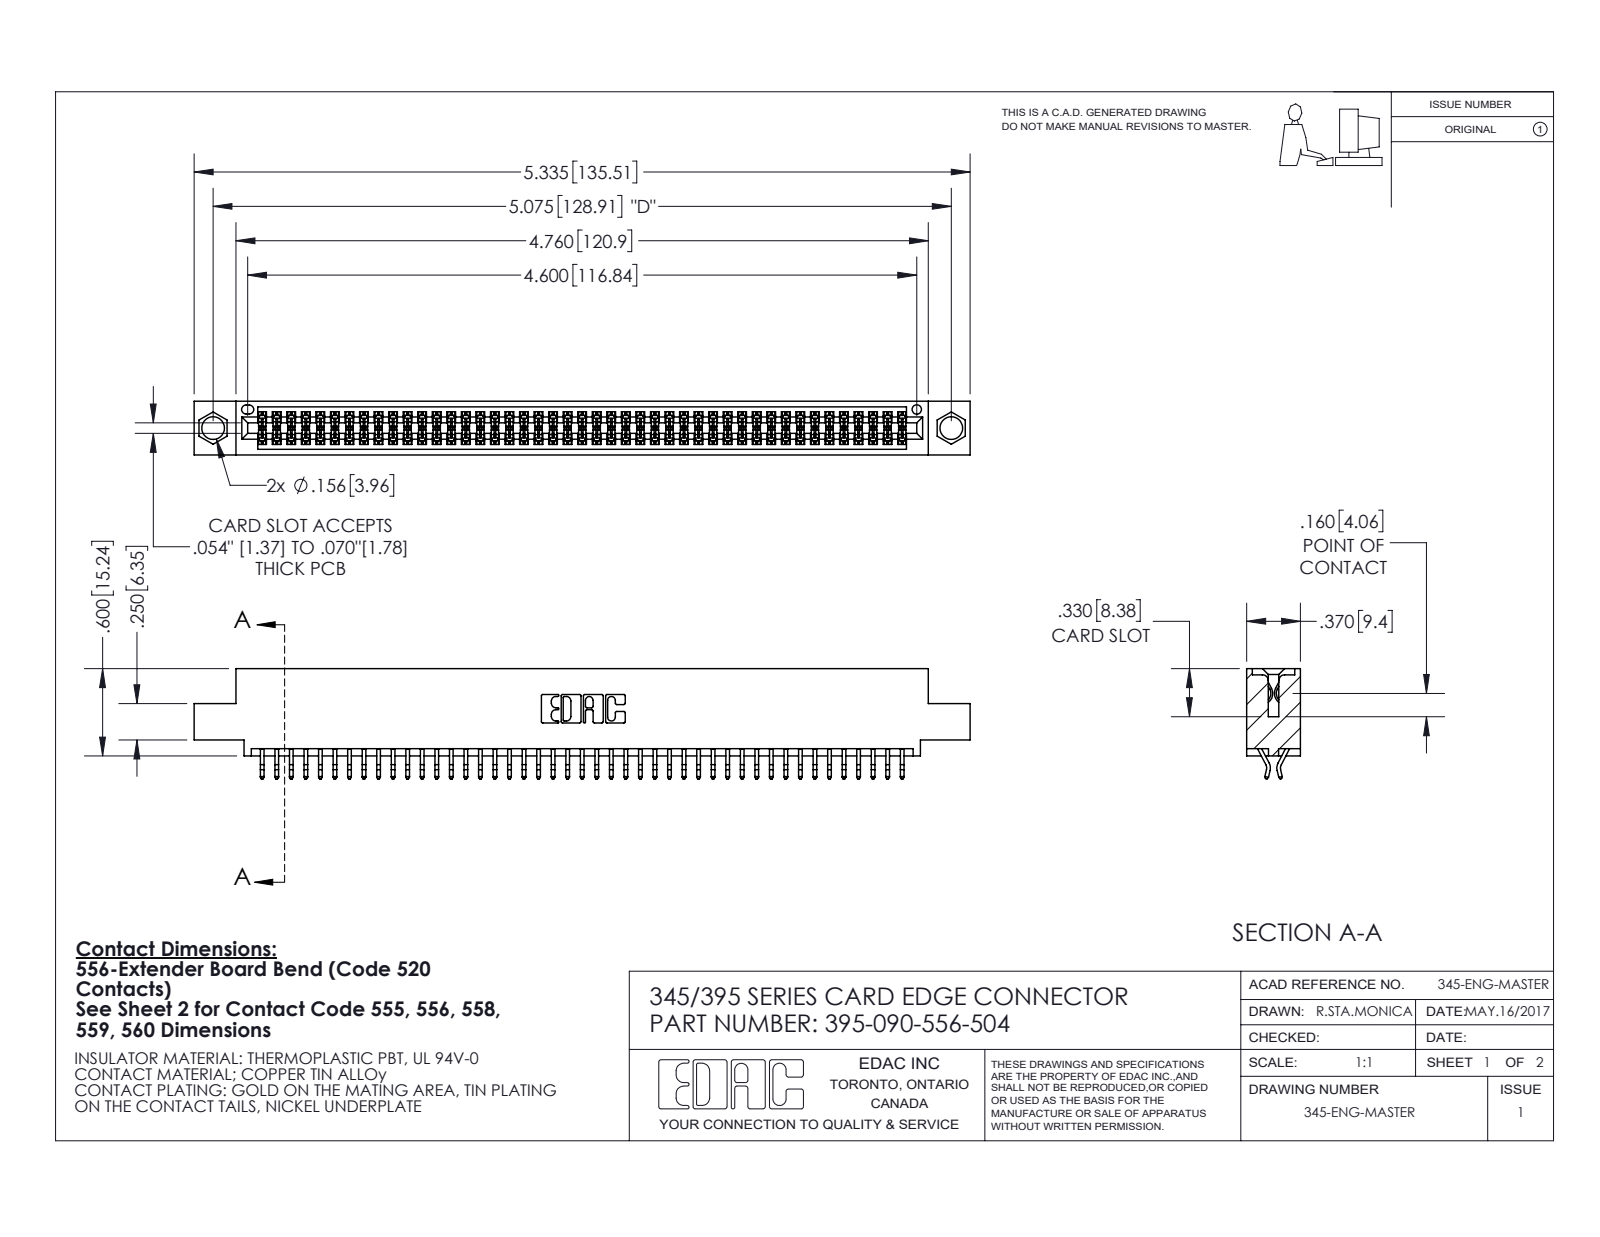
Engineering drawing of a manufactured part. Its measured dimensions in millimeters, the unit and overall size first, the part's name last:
Units: millimetres
Overall size (bounding box): 135.5 × 19.2 × 9.4
Round holes (diameter × count): ⌀4 ×2, ⌀1.6 ×1
Partial cylindrical surfaces — rounded edges, fillets, slot ends (radius × count): R0.2 ×180, R0.3 ×22, R0.2 ×6, R0.8 ×6, R0.7 ×3, R0.3 ×2, R0.4 ×2, R0.5 ×2
Main face-to-face distances: 7.6, 1.8, 9.4, 5.1, 0.6, 2.5, 6.9, 5.7, 4.4, 3.8
Hole centre spacings: 6.9, 122.9, 128.9
Volume: 13 000 mm³ · Surface area: 19 150 mm²
Bodies: 91 solids, 5184 faces (3428 planar, 1756 cylindrical, 0 other)
Part name (STEP PRODUCT): 345-292-001_556 Tail; 345 Part_0.110 Offset - 0.156 Dia-TI; 395-090-556-504
STEP written by: SolidWorks 2020 (CONFIG_CONTROL_DESIGN)
